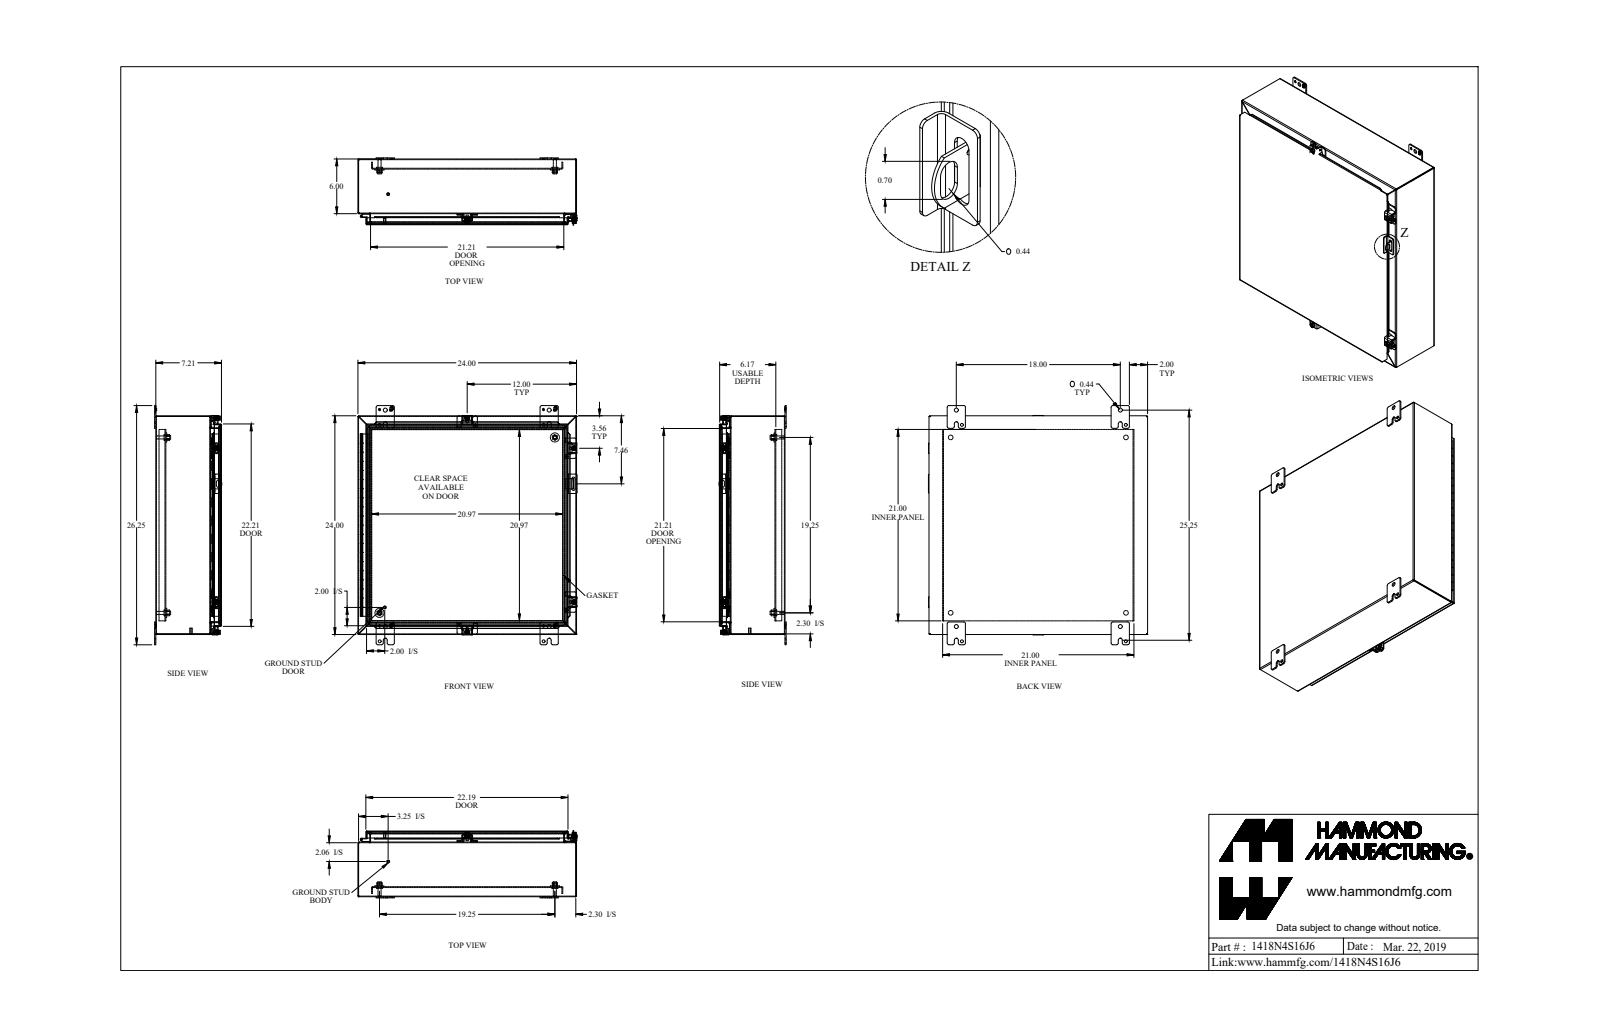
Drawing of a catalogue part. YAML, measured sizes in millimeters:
part_name: "1418N4S16J6_Default"
step_written_by: "SolidWorks 2019 (CONFIG_CONTROL_DESIGN)"
units: millimeters
bodies: {solids: 39, faces: 1373, planar: 746, cylindrical: 493, other: 134}
overall_size: [666.8, 611.2, 187.3]
volume: 3263000
surface_area: 3364000
round_holes:
  - {diameter: 5.4, count: 4}
  - {diameter: 6.7, count: 4}
  - {diameter: 8, count: 4}
  - {diameter: 9.5, count: 4}
  - {diameter: 11.1, count: 4}
  - {diameter: 12.7, count: 4}
  - {diameter: 7.8, count: 2}
  - {diameter: 11.3, count: 2}
  - {diameter: 2.8, count: 1}
  - {diameter: 3.2, count: 1}
round_bosses_or_shafts:
  - {diameter: 16.5, count: 4}
  - {diameter: 12.7, count: 4}
  - {diameter: 9.9, count: 4}
  - {diameter: 9.5, count: 4}
  - {diameter: 8.4, count: 4}
  - {diameter: 6.2, count: 4}
  - {diameter: 25.4, count: 2}
  - {diameter: 8, count: 2}
partial_cylinders:
  - {radius: 4.8, count: 26}
  - {radius: 0.9, count: 24}
  - {radius: 2.7, count: 24}
  - {radius: 1.2, count: 21}
  - {radius: 3.6, count: 21}
  - {radius: 6.4, count: 20}
  - {radius: 3.2, count: 12}
  - {radius: 1.1, count: 8}
face_to_face_distances: [1.8, 1.8, 607.8, 179.5, 181.3, 181.3, 183.1, 23.8, 2.4, 25.6]
hole_center_spacings: [489, 250.4, 457.2, 44.1, 595.4, 603.3, 691.5, 756.9]
